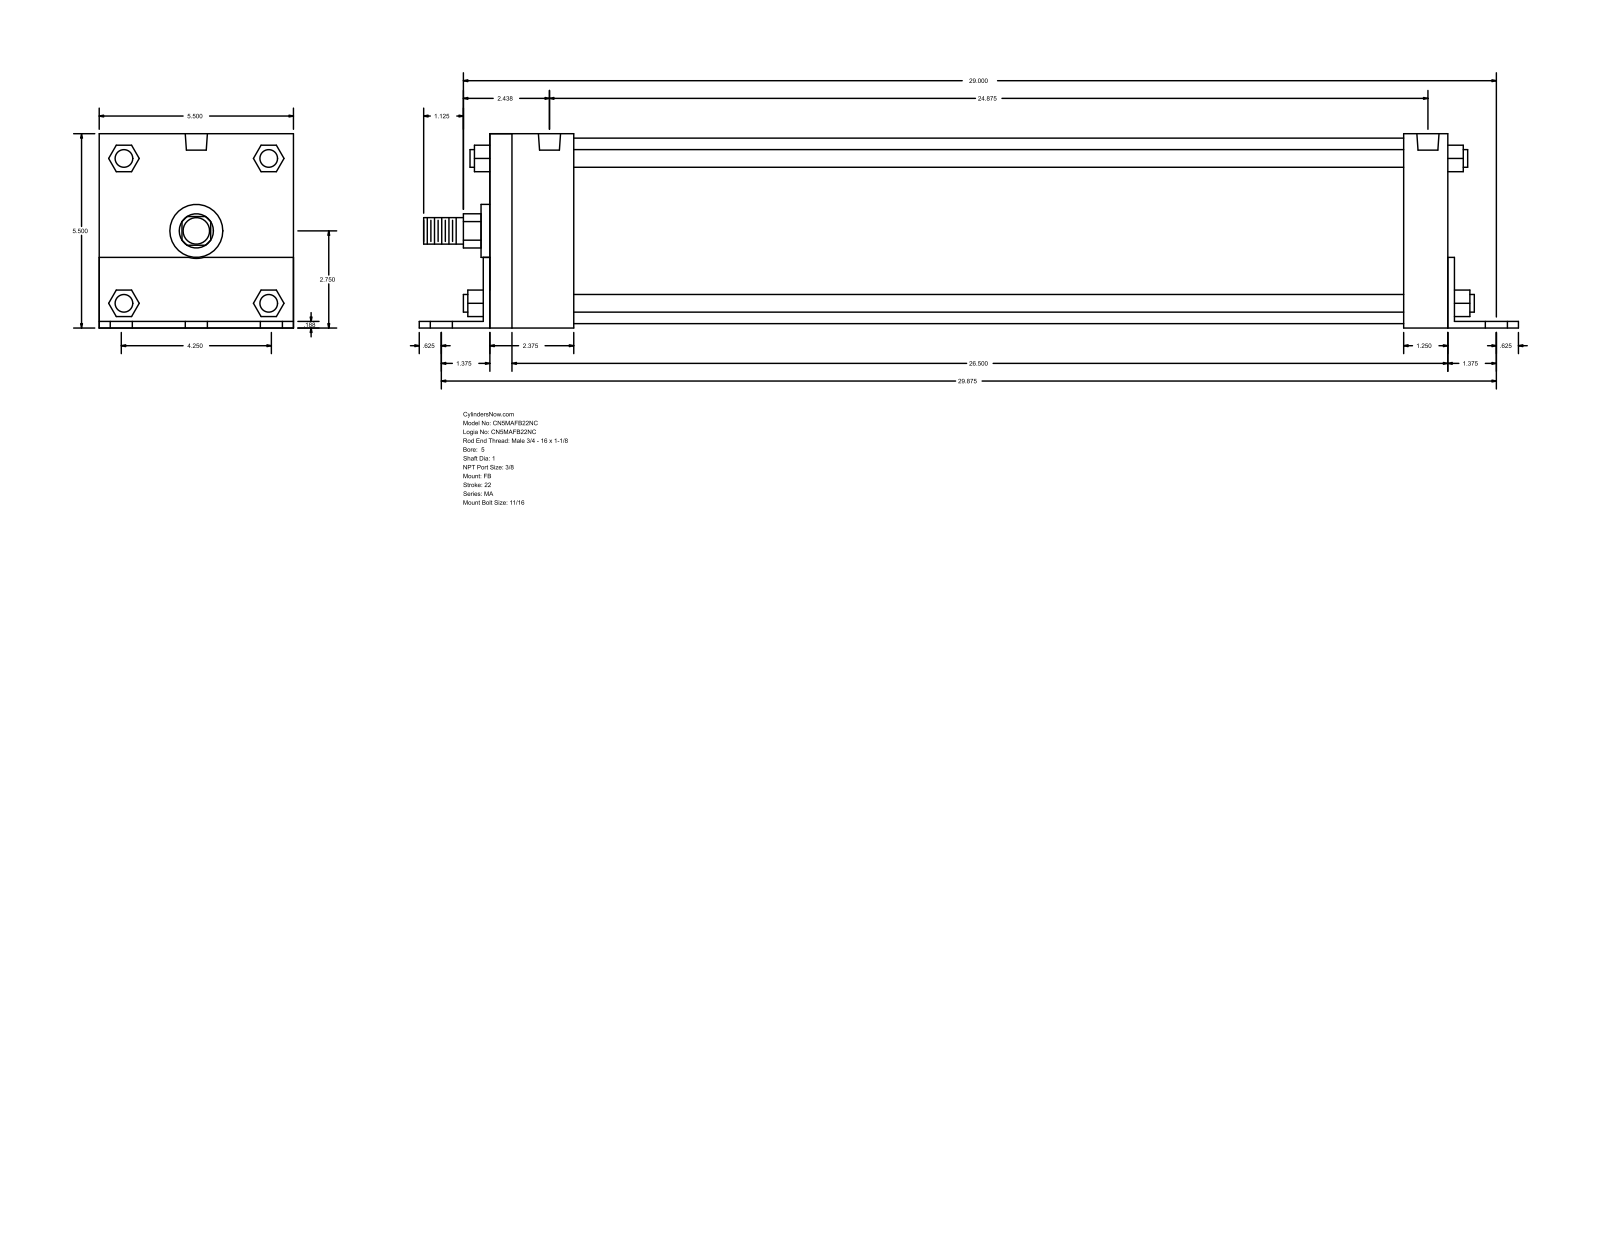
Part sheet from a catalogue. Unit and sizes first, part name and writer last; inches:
Units: inches
Overall size (bounding box): 31.125 × 5.502 × 5.5
Round holes (diameter × count): ⌀0.687 ×6, ⌀0.437 ×4, ⌀0.627 ×2
Round bosses / shafts (diameter × count): ⌀0.5 ×4, ⌀5.25 ×1, ⌀1.5 ×1, ⌀1 ×1, ⌀0.75 ×1
Partial cylindrical surfaces — rounded edges, fillets, slot ends (radius × count): R0.484 ×1, R0.78 ×1
Main face-to-face distances: 5.5, 0.187, 5.502, 0.185, 5.315, 27.125, 0.188, 27.313, 27.312, 27.5
Hole centre spacings: 2.125, 29.951, 29.875, 0.187, 2.876, 3.005, 3.728, 3.883
Bodies: 0 solids, 140 faces (105 planar, 35 cylindrical, 0 other)
Part name (STEP PRODUCT): MA_FB__0500_1
STEP written by: GSSL Pune (CONFIG_CONTROL_DESIGN)
